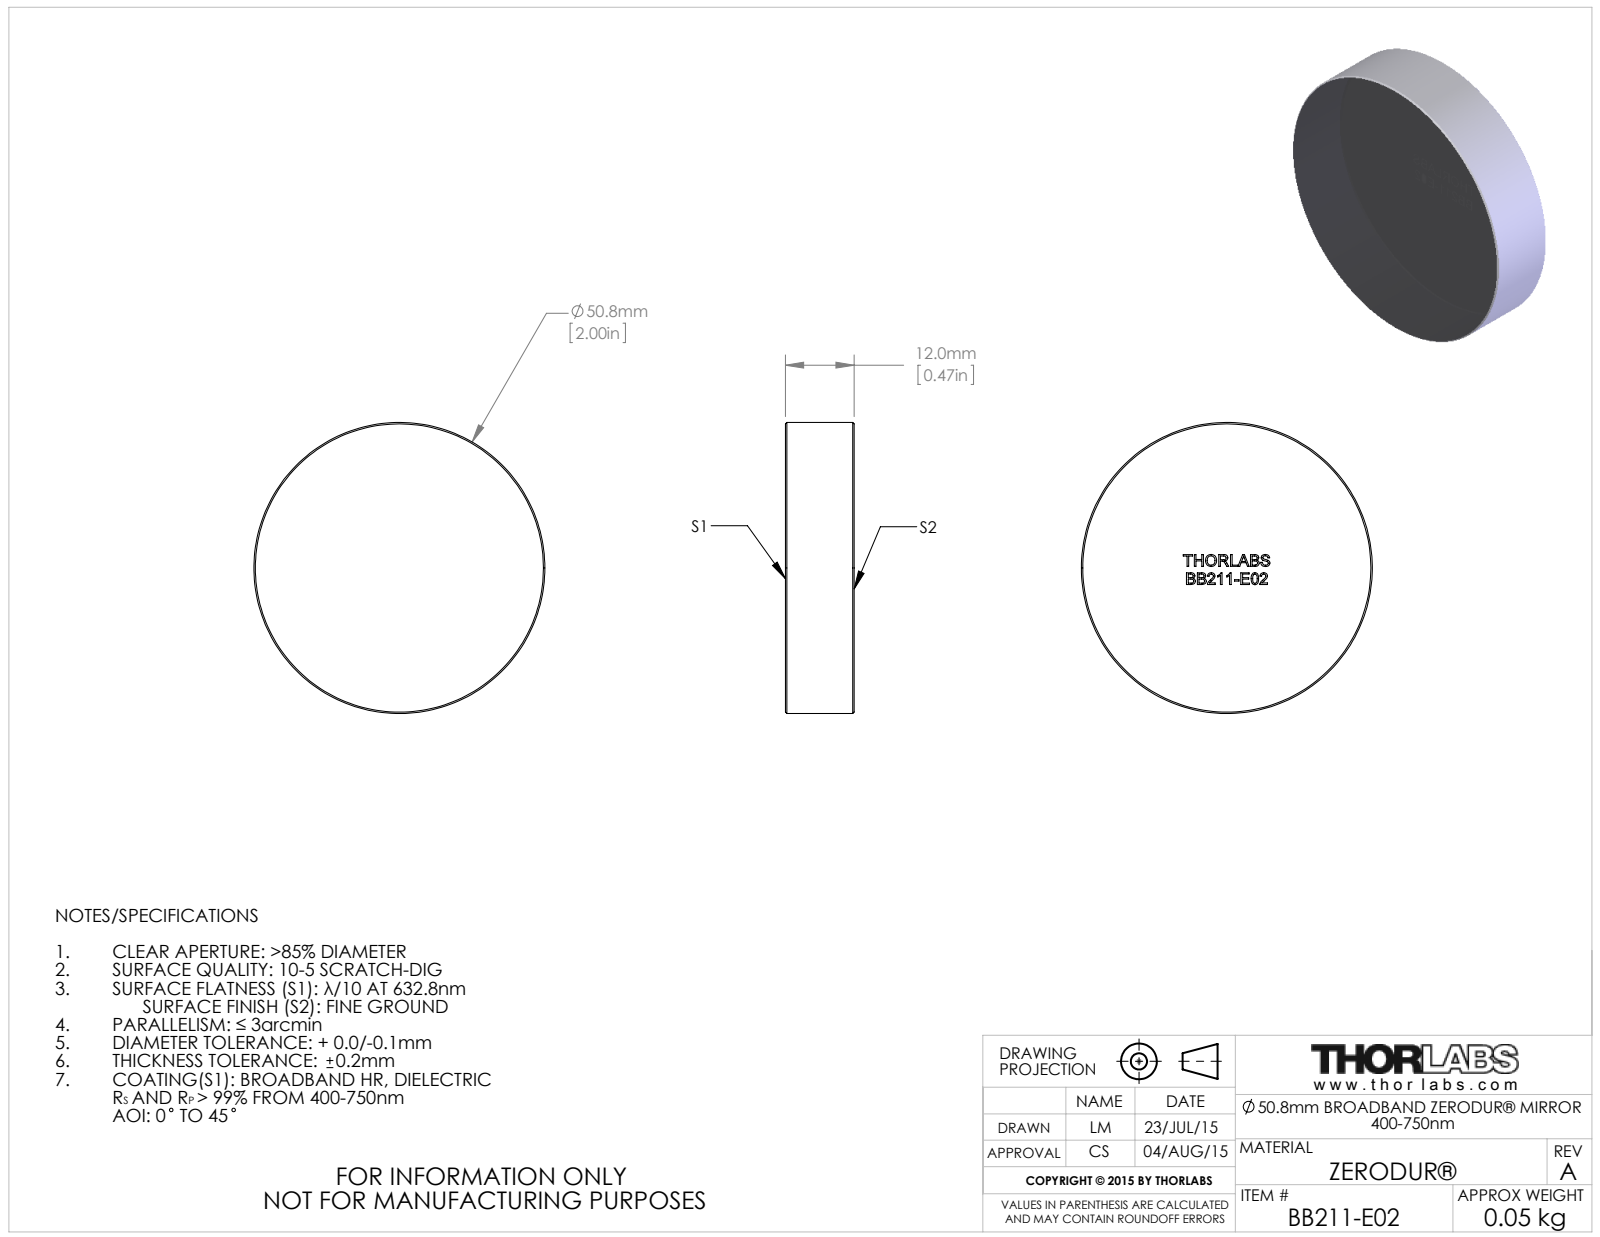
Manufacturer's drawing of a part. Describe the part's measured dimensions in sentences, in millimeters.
The part is named "TTN045205-E0W". Its 3-D file was written by "SolidWorks 2014 (CONFIG_CONTROL_DESIGN)". It is 1 solid with 240 faces: 140 planar, 2 cylindrical and 98 other. Overall it measures 50.8 by 50.8 by 12 millimeters. Its volume is 24 312 cubic millimeters and its surface area 5 922 square millimeters. Round bosses or shafts: 1 of diameter 50.8. The main face-to-face distances are 12, 3.16, 1.58, 2.05, 5.53, 4.03, 7.59, 0.87, 7.68, 1.35.
